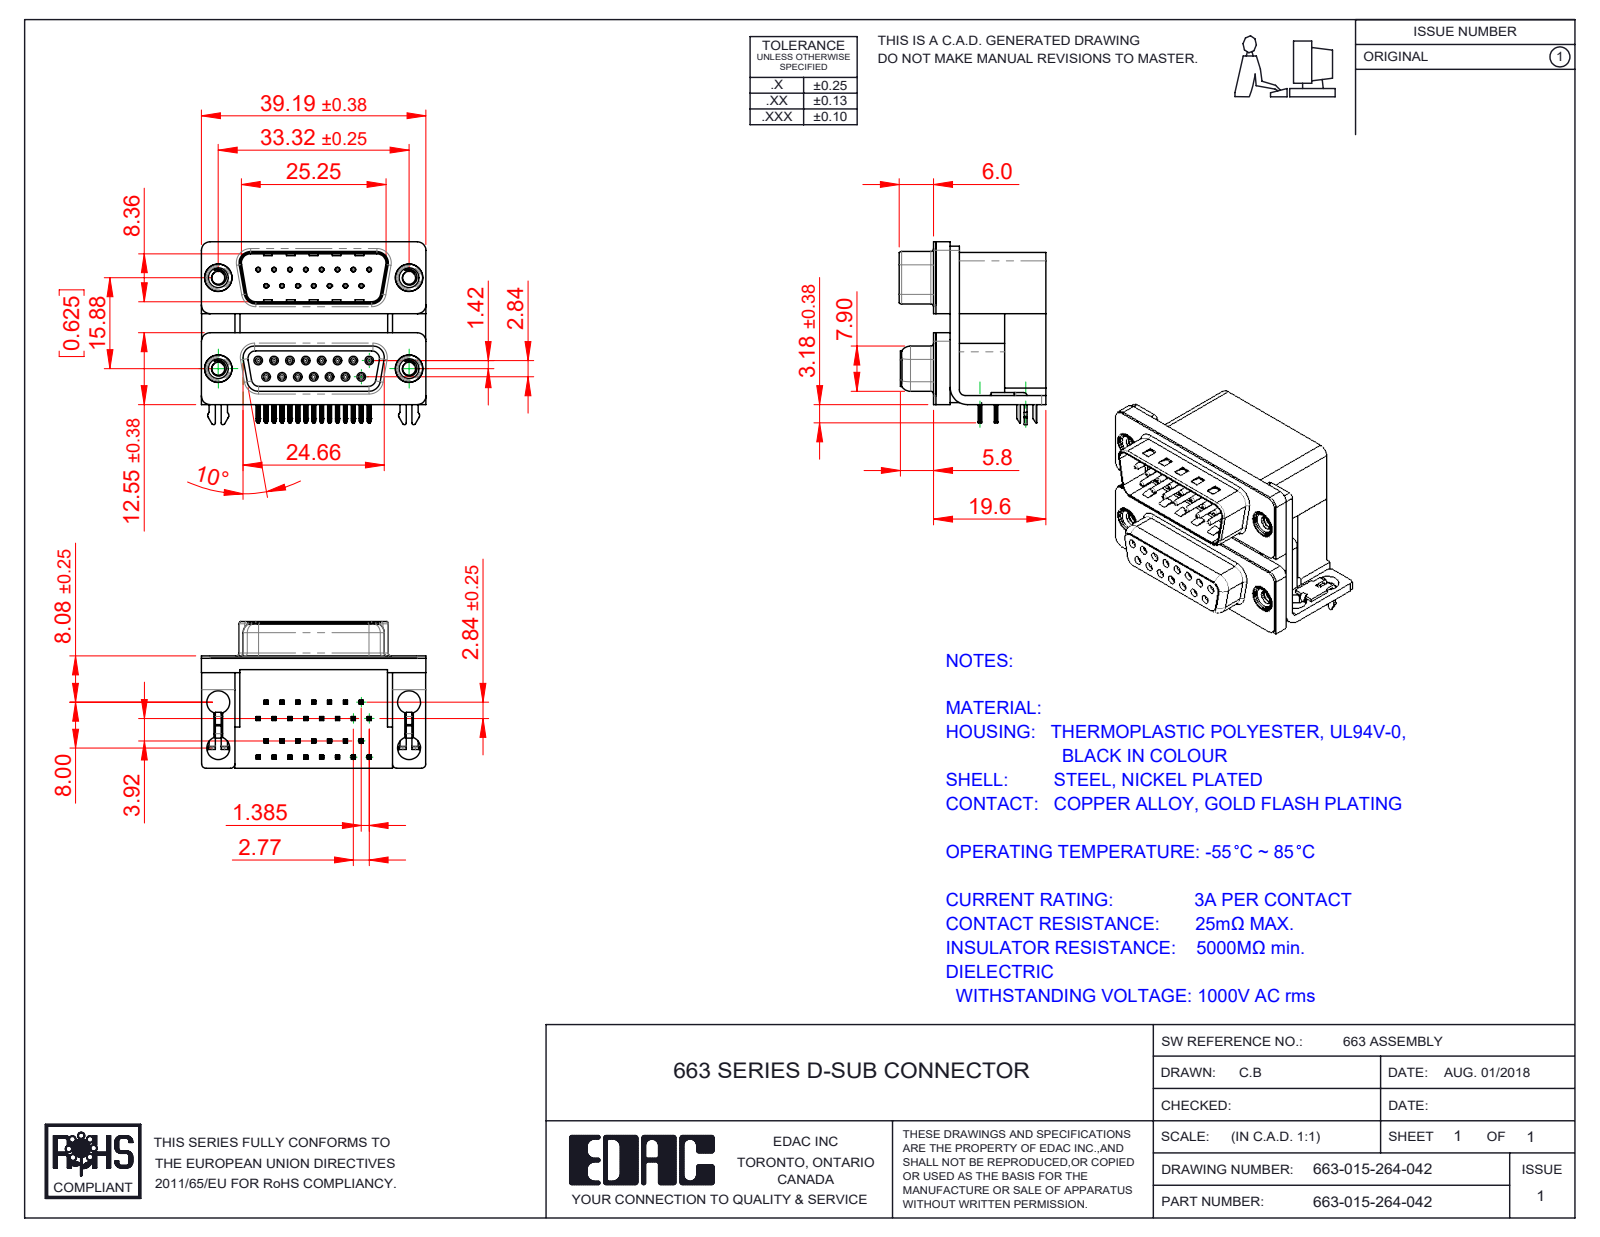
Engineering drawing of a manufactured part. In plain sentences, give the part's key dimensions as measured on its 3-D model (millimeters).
The part is named "663 Contact Top Upper_L; 663 2 Prong Board Lock_4; 663 Housing Lower_15 Contacts; 663-015-264-042 (+8 more)". Its 3-D file was written by "SolidWorks 2020 (CONFIG_CONTROL_DESIGN)". It is 43 solids with 4020 faces: 2093 planar, 1044 cylindrical and 883 other. Overall it measures 39.19 by 31.93 by 25.6 millimeters. Its volume is 14 586 cubic millimeters and its surface area 16 316 square millimeters. Round holes: 30 of diameter 0.8, 15 of diameter 0.35, 15 of diameter 0.9, 8 of diameter 4, 4 of diameter 2.26, 4 of diameter 3.5, 4 of diameter 4.8, 4 of diameter 5. Round bosses or shafts: 15 of diameter 1.2, 15 of diameter 0.75, 4 of diameter 4.9, 4 of diameter 4.75, 4 of diameter 3.9. Partial cylindrical surfaces (rounded edges, fillets, slot ends): 121 of radius 0.1, 66 of radius 0.25, 60 of radius 0.15, 30 of radius 0.12, 30 of radius 0.35, 16 of radius 0.5, 16 of radius 1.5, 15 of radius 0.34. The main face-to-face distances are 0.4, 19.2, 16.7, 2.5, 10.7, 7.2, 12, 9.5, 2.9, 19.6. The hole center spacings are 3.16, 16.12, 2.77, 16.82, 5.54, 8.31, 15.88, 17.92.
